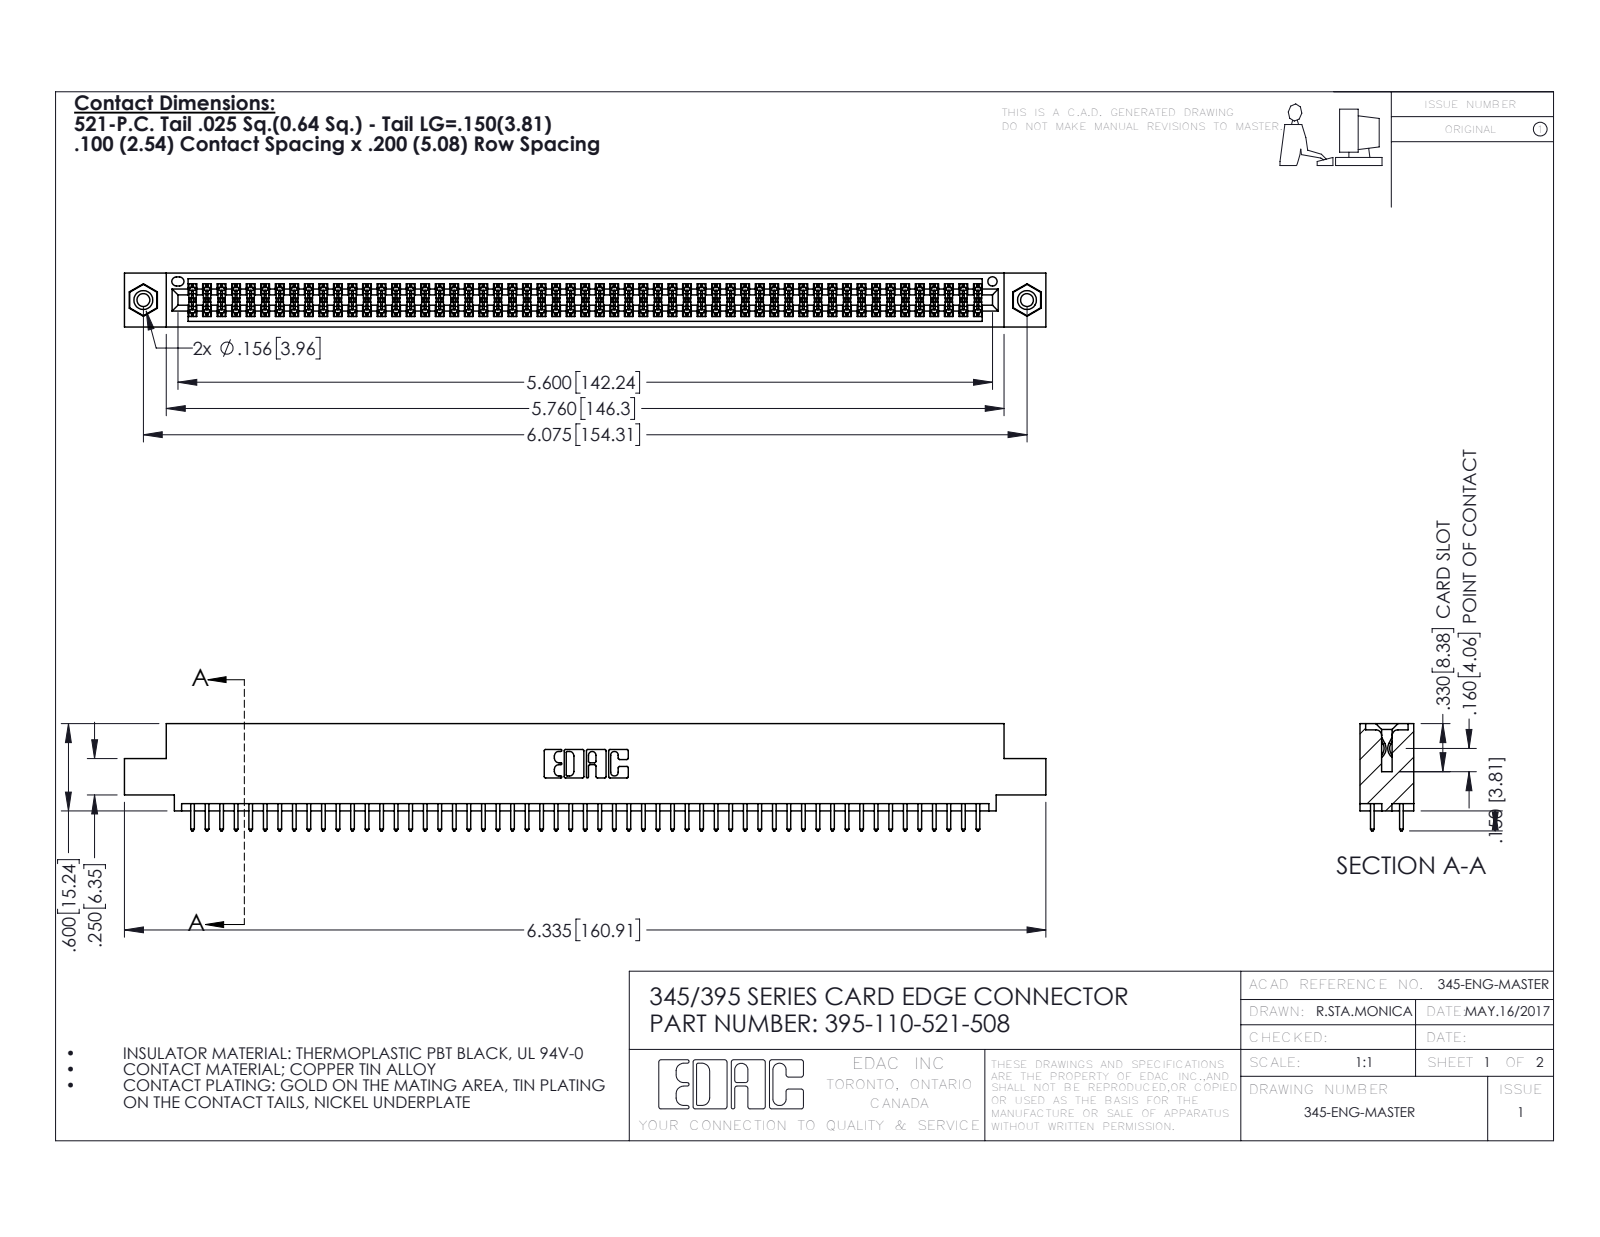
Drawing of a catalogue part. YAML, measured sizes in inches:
part_name: "345-292-001_345-293-121; 395-110-521-508; 345 Part_0.110 Offset - 0.156 Dia-TI; 345-250-001_345-250-003-102"
step_written_by: "SolidWorks 2016 (CONFIG_CONTROL_DESIGN)"
units: inches
bodies: {solids: 113, faces: 5690, planar: 3746, cylindrical: 1928, other: 16}
overall_size: [6.335, 0.737, 0.37]
volume: 0.954
surface_area: 35.91
round_holes:
  - {diameter: 0.089, count: 2}
  - {diameter: 0.125, count: 2}
  - {diameter: 0.156, count: 2}
  - {diameter: 0.064, count: 1}
round_bosses_or_shafts:
  - {diameter: 0.155, count: 2}
partial_cylinders:
  - {radius: 0.006, count: 165}
  - {radius: 0.01, count: 110}
  - {radius: 0.01, count: 22}
  - {radius: 0.007, count: 6}
  - {radius: 0.031, count: 6}
  - {radius: 0.026, count: 3}
  - {radius: 0.014, count: 2}
  - {radius: 0.019, count: 2}
face_to_face_distances: [0.072, 0.298, 0.2, 0.098, 0.272, 0.025, 0.37, 0.225, 0.175, 0.149]
hole_center_spacings: [0.27, 5.839, 6.075]
